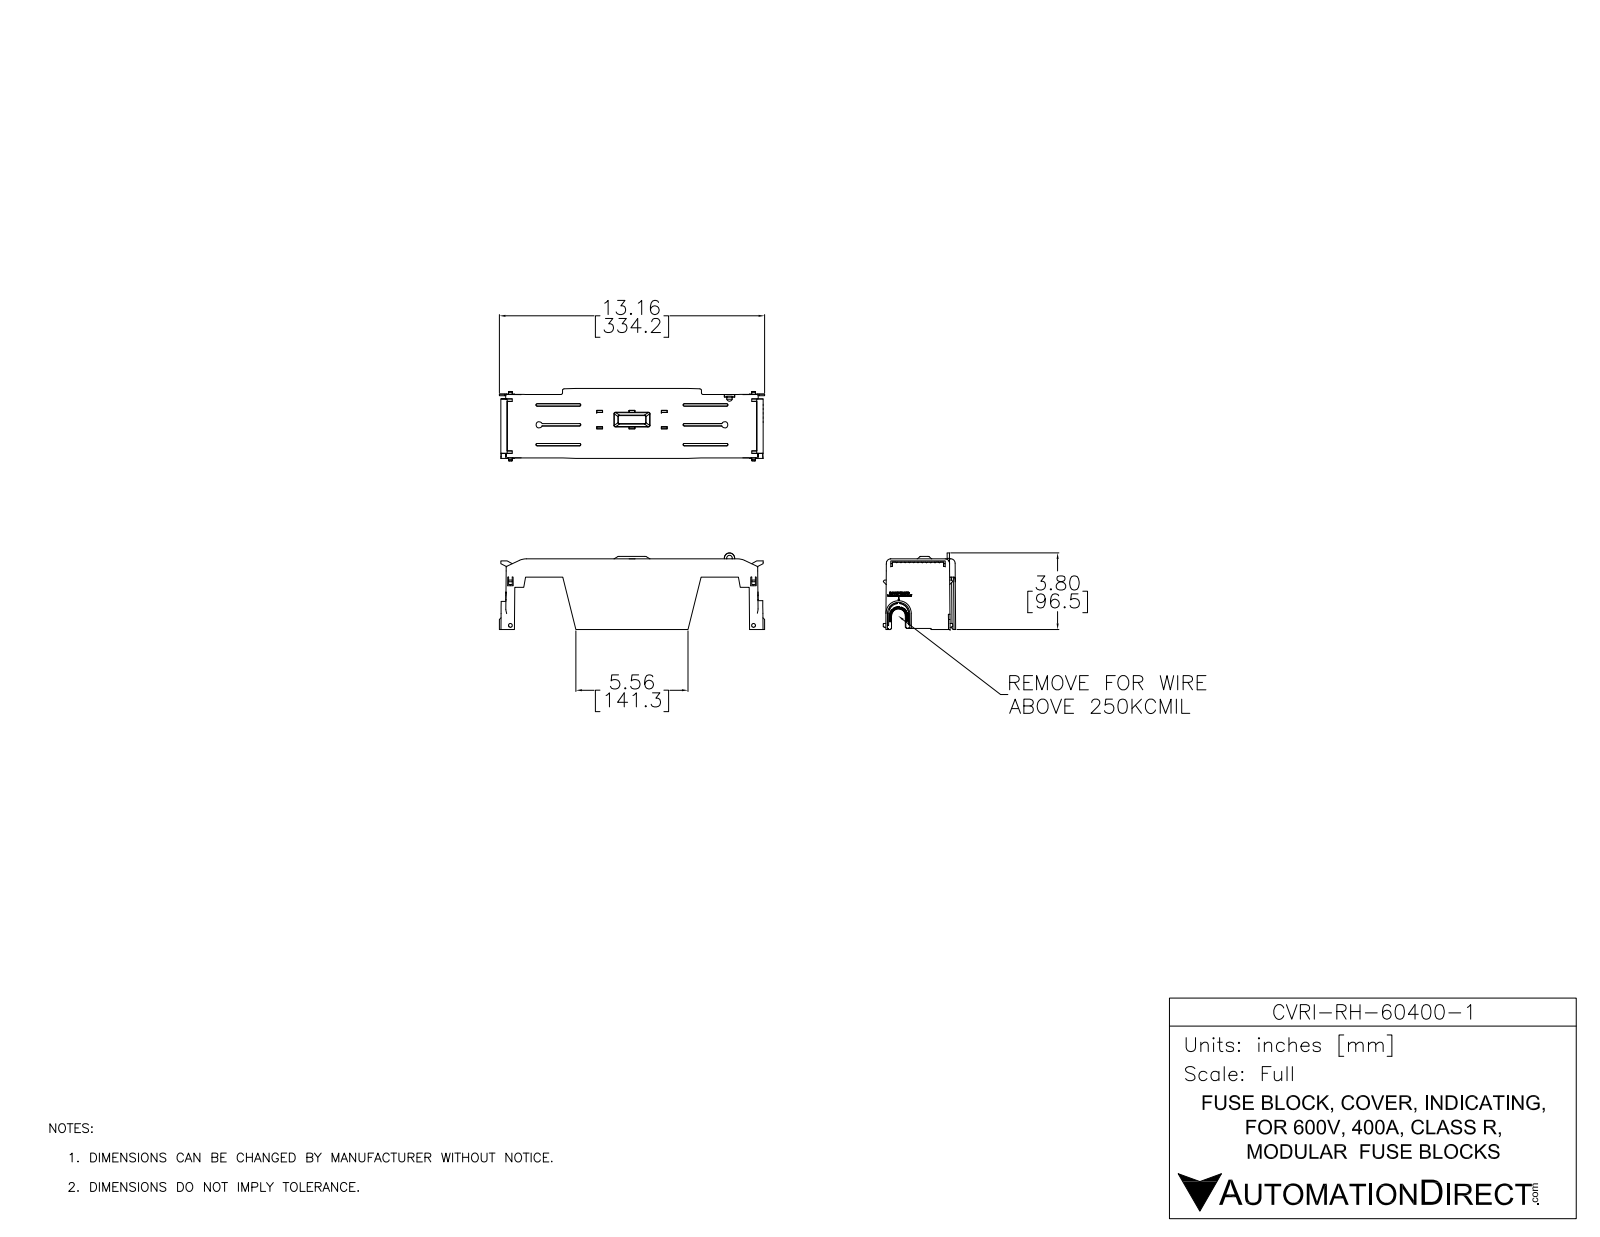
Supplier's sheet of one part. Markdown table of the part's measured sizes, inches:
| quantity | value |
| --- | --- |
| part name | CVRI-RH-60400-1 |
| STEP written by | SolidWorks 2017 (AUTOMOTIVE_DESIGN) |
| units | inches |
| bodies | 1 solid, 2374 faces (1611 planar, 104 cylindrical, 659 other) |
| overall size | 13.158 × 3.8 × 3.594 |
| volume | 10.25 in³ |
| surface area | 270.7 in² |
| round holes (diameter × count) | 0.276 × 1 |
| partial cylindrical surfaces (radius × count) | 0.039 × 18, 0.079 × 8, 0.118 × 8, 0.138 × 8, 0.217 × 8, 0.01 × 2, 0.02 × 2, 0.04 × 2 |
| main face-to-face distances | 0.079, 0.276, 0.197, 0.354, 0.118, 0.803, 1.472, 0.669, 0.236, 4.974 |
